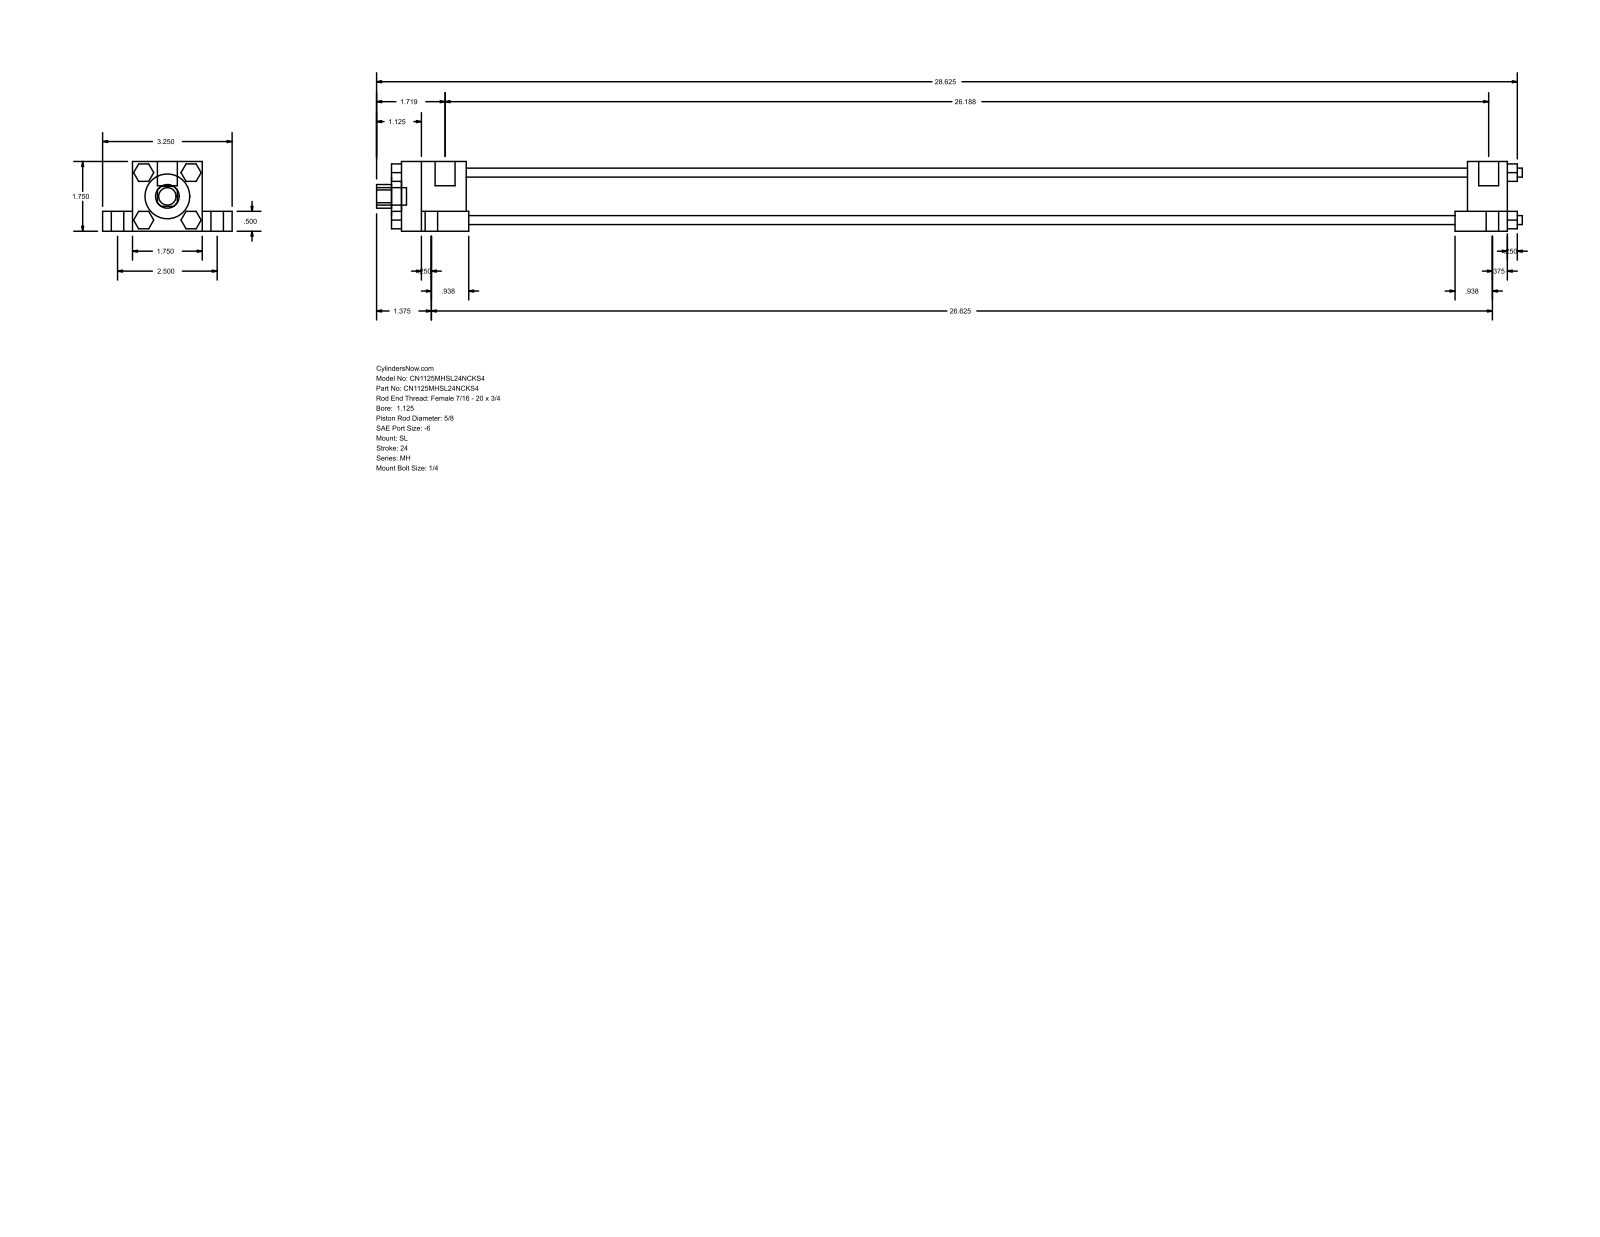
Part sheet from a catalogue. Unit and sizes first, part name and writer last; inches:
Units: inches
Overall size (bounding box): 28.75 × 3.25 × 1.75
Round holes (diameter × count): ⌀0.625 ×1, ⌀1.125 ×1, ⌀1.375 ×1
Round bosses / shafts (diameter × count): ⌀0.563 ×4, ⌀0.313 ×4, ⌀0.225 ×4, ⌀0.219 ×4, ⌀0.5 ×2, ⌀0.437 ×1
Partial cylindrical surfaces — rounded edges, fillets, slot ends (radius × count): R0.297 ×1
Main face-to-face distances: 1.75, 0.75, 0.5, 1.25, 2.5, 0.25, 28, 0.437, 1.313, 25.938
Bodies: 0 solids, 150 faces (114 planar, 36 cylindrical, 0 other)
Part name (STEP PRODUCT): MH_SL__0112_0.625
STEP written by: GSSL Pune (CONFIG_CONTROL_DESIGN)
